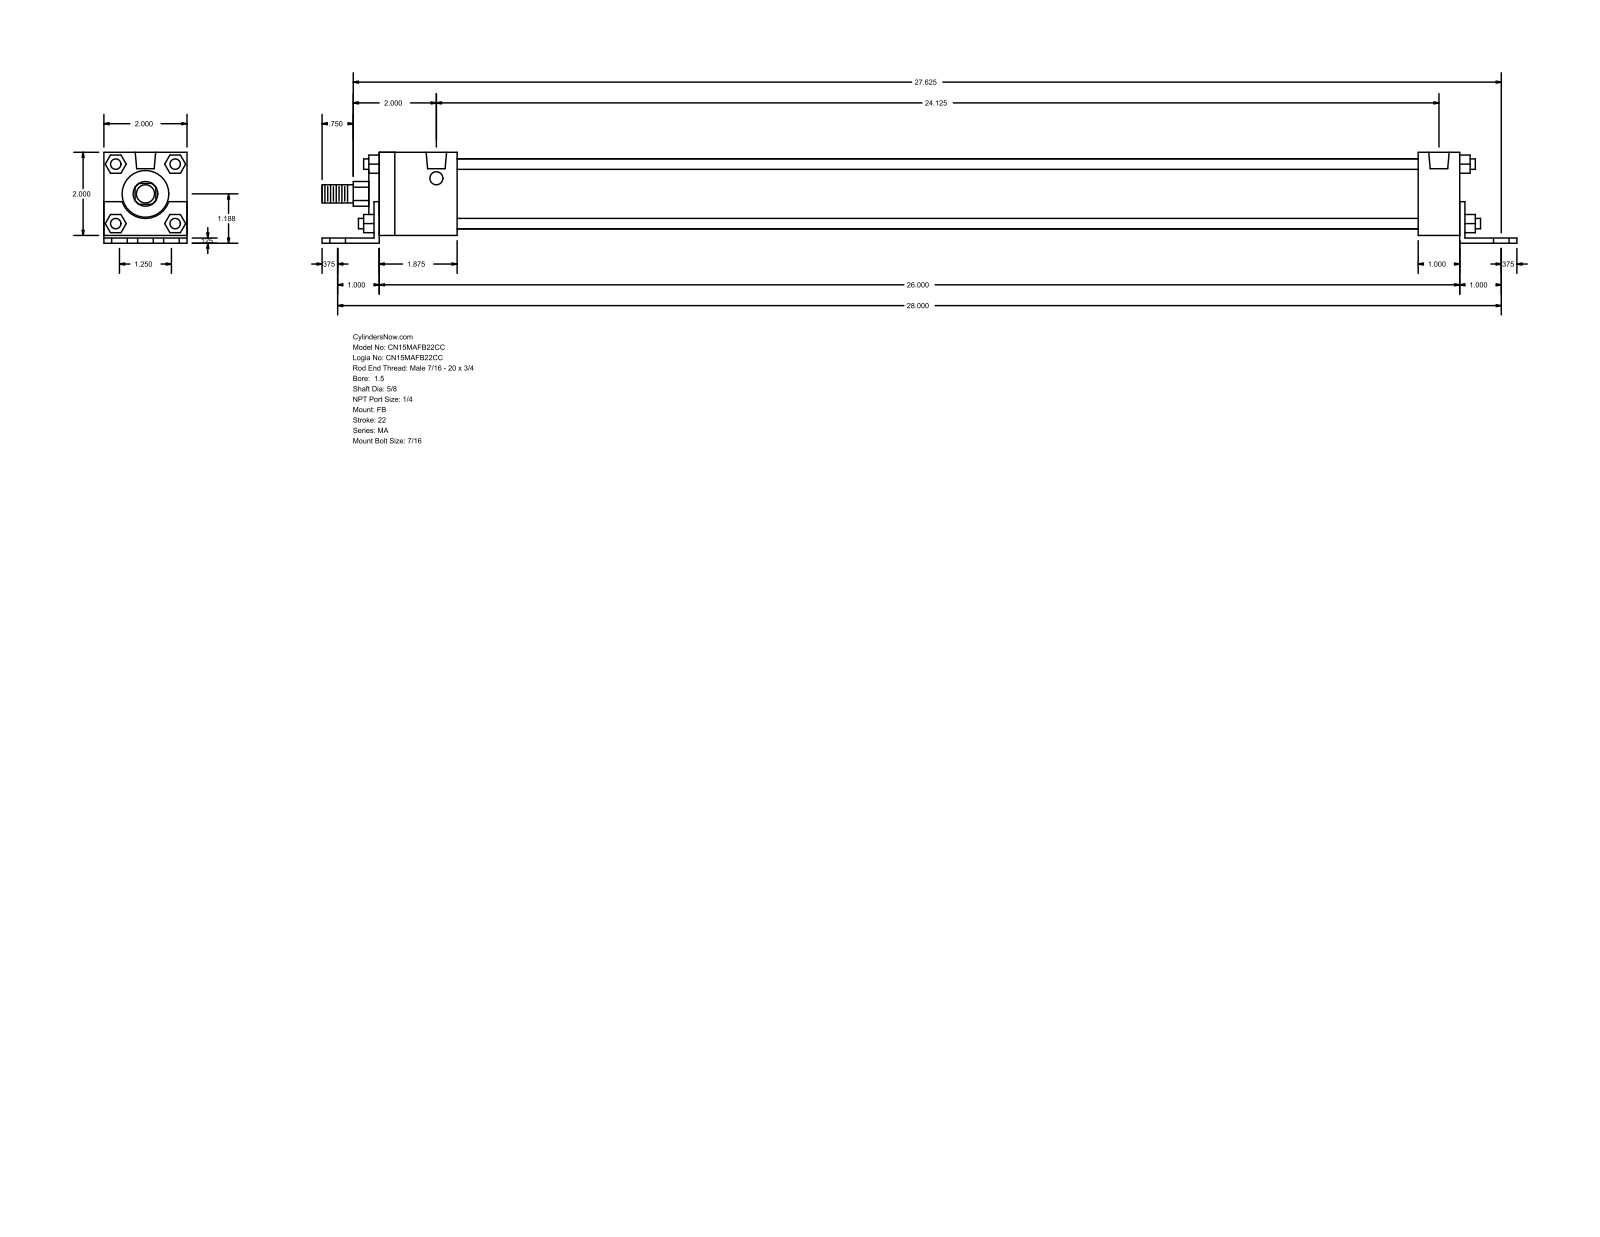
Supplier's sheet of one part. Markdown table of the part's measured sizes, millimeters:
| quantity | value |
| --- | --- |
| part name | MA_FB__0150_0.625 |
| STEP written by | GSSL Pune (CONFIG_CONTROL_DESIGN) |
| units | millimeters |
| bodies | 0 solids, 140 faces (105 planar, 35 cylindrical, 0 other) |
| overall size | 730.25 × 55.56 × 50.8 |
| round holes (diameter × count) | 11.11 × 6, 7.94 × 4, 12.49 × 2 |
| round bosses / shafts (diameter × count) | 6.35 × 4, 42.93 × 1, 28.57 × 1, 15.88 × 1, 11.11 × 1 |
| partial cylindrical surfaces (radius × count) | 7.54 × 1, 15.05 × 1 |
| main face-to-face distances | 50.8, 3.17, 4.76, 55.56, 1.59, 52.39, 3.18, 663.57, 6.35, 669.92 |
| hole center spacings | 15.88, 711.38, 711.2, 31.76, 41.27, 62.38, 612.78, 651.06 |
